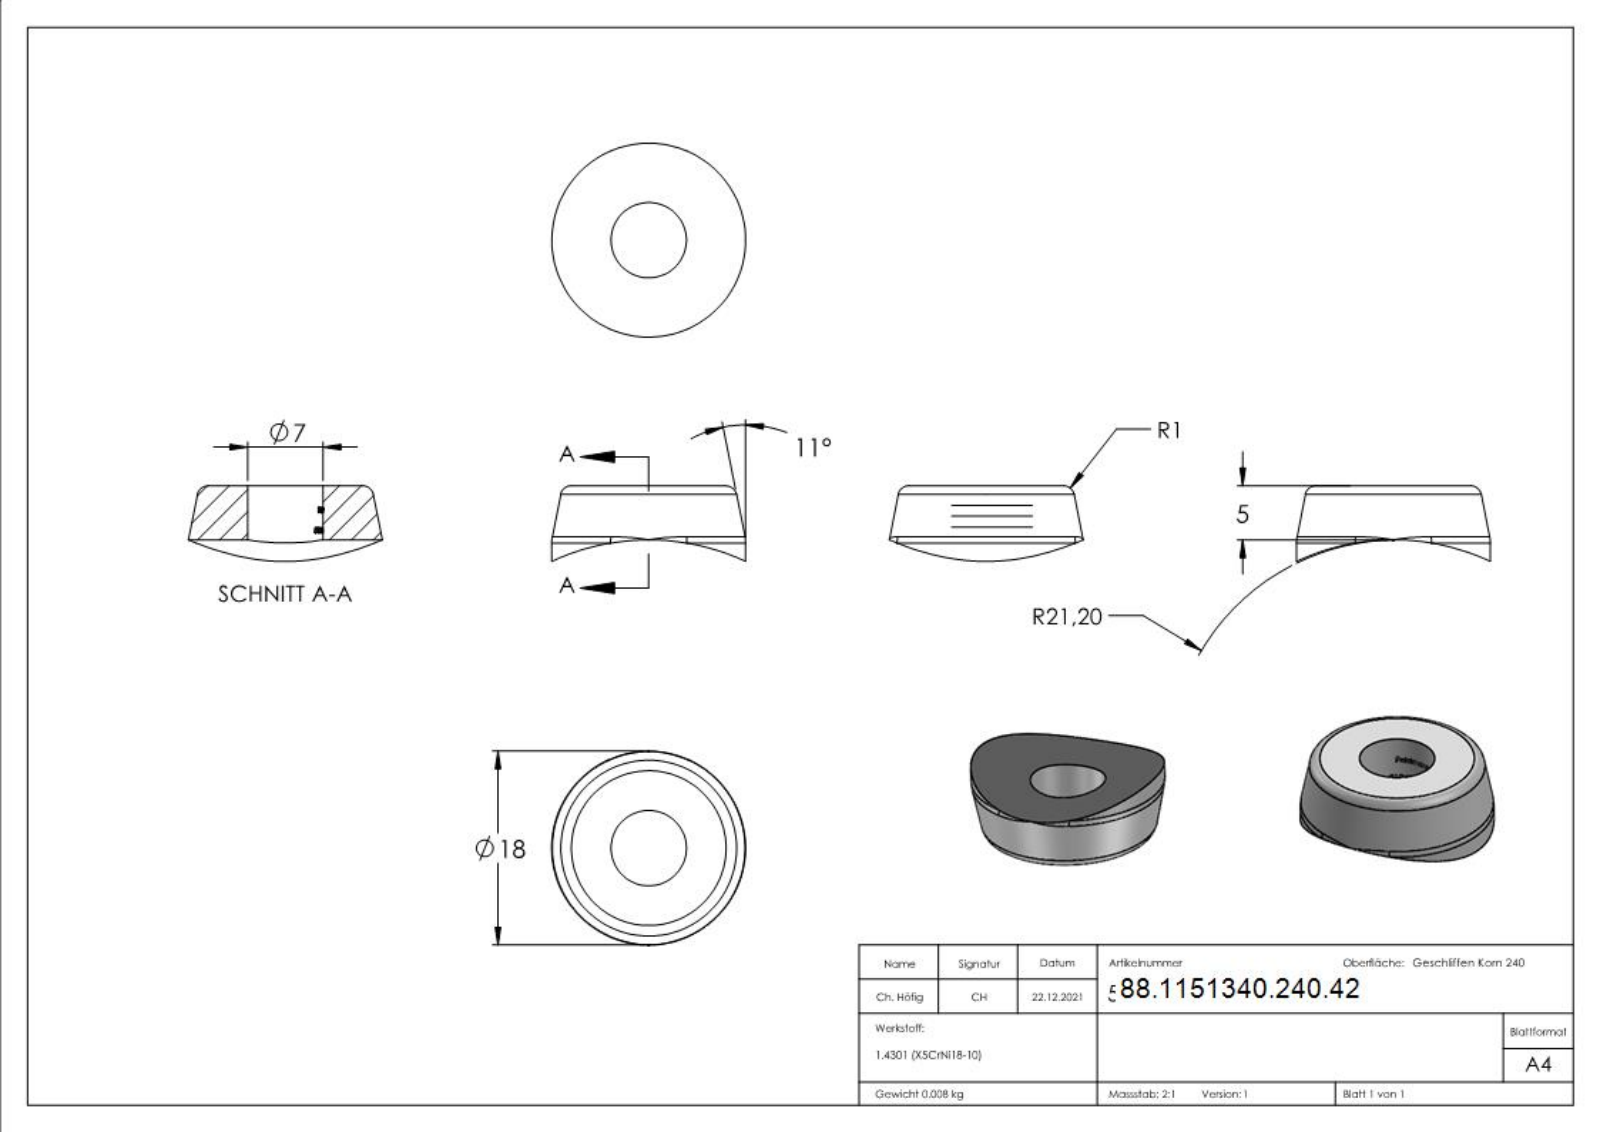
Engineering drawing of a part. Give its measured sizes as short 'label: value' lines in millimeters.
name: 51340-240-42
written by: SolidWorks 2018 (CONFIG_CONTROL_DESIGN)
unit: mm
bodies: 1 solid, 273 faces (129 planar, 33 cylindrical, 111 other)
size: 18 × 18 × 7
volume: 1 059 mm³; area: 817 mm²
holes: 1× ⌀7
rounds: 1× R3.6, 1× R9, 1× R21.2
face distances: 1.59, 1.88, 2.14, 1.83, 0.35, 1.64, 1.94, 2.18, 4.21, 0.88
